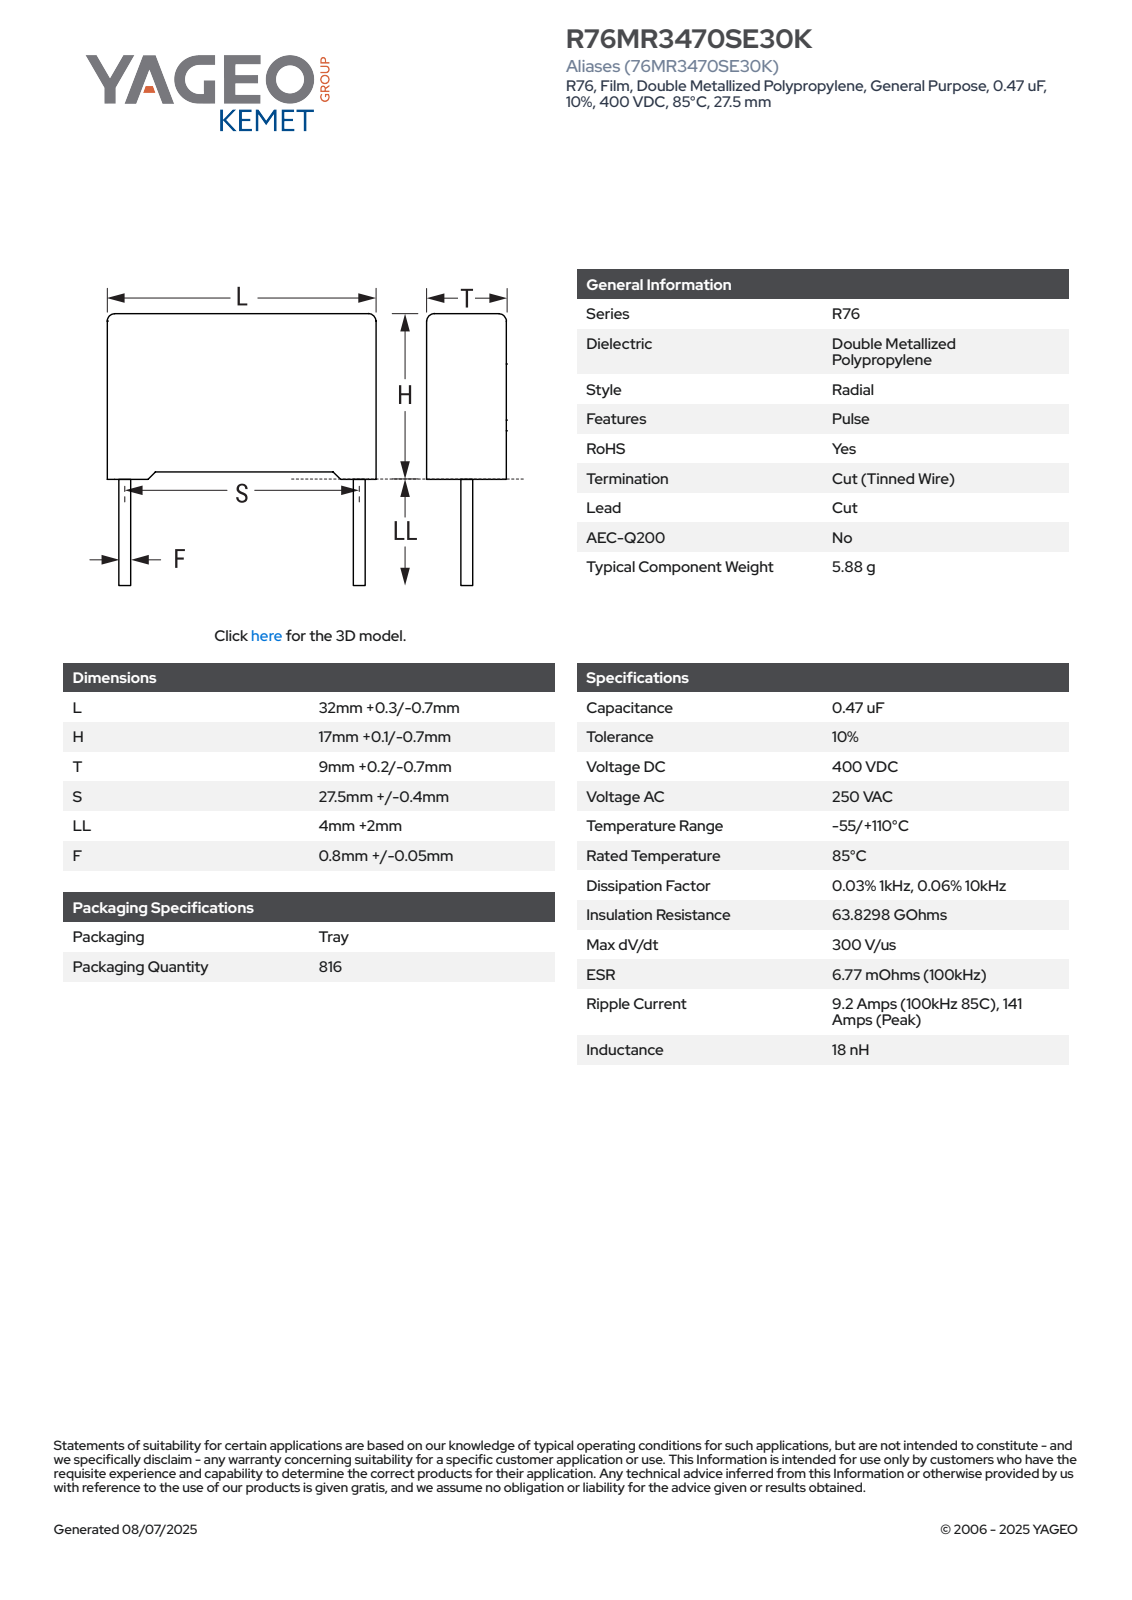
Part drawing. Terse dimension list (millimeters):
name: CFR_RB2_32X17X9_L32.3H17.1T9.2S27.5LL6F0.85
written by: SolidWorks 2021 (AUTOMOTIVE_DESIGN)
unit: mm
bodies: 4 solids, 85 faces (77 planar, 8 cylindrical, 0 other)
size: 32.3 × 23.1 × 9.21
volume: 4 896 mm³; area: 2 111 mm²
bosses: 2× ⌀0.85
rounds: 4× R0.5
face distances: 9.2, 16.35, 32.3, 16.51, 0.59, 0.75, 17.1, 1.08, 9.21, 8.12
